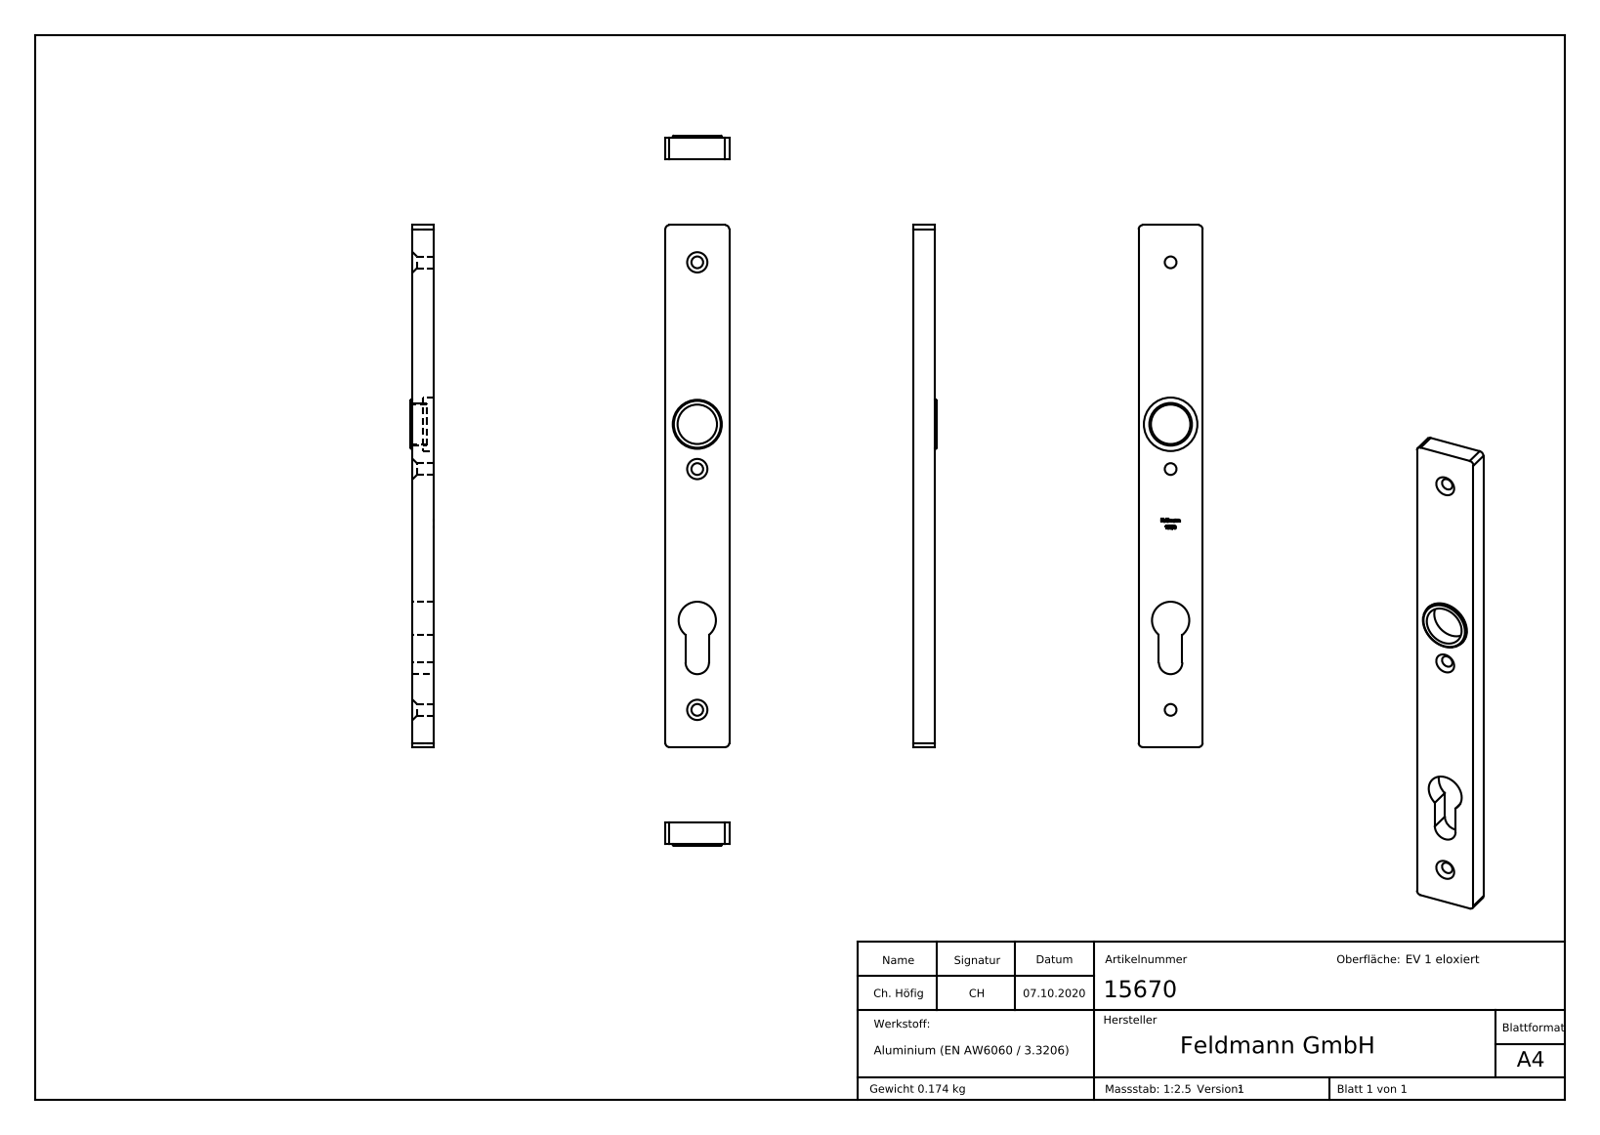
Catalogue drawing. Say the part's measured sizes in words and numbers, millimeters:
The part is named "AMF Schliessblech Konfig Teil2_15552 Teil2; AMF Schliessblech Konfig Teil2; AMF Schliessblech Konfig Teil1; 15670 (+1 more)". Its 3-D file was written by "SolidWorks 2018 (CONFIG_CONTROL_DESIGN)". It is 2 solids with 211 faces: 105 planar, 24 cylindrical and 82 other. Overall it measures 245 by 30 by 11 millimeters. Its volume is 64 858 cubic millimeters and its surface area 21 802 square millimeters. Round holes: 3 of diameter 5.5, 1 of diameter 18.5, 1 of diameter 20, 1 of diameter 25.1. Round bosses or shafts: 1 of diameter 23. Partial cylindrical surfaces (rounded edges, fillets, slot ends): 4 of radius 2, 1 of radius 5.5, 1 of radius 8.75. The main face-to-face distances are 10, 30, 5, 245, 9.5, 20.5, 11, 6, 1, 3.5. The hole center spacings are 21, 76, 97, 113, 134, 210.
